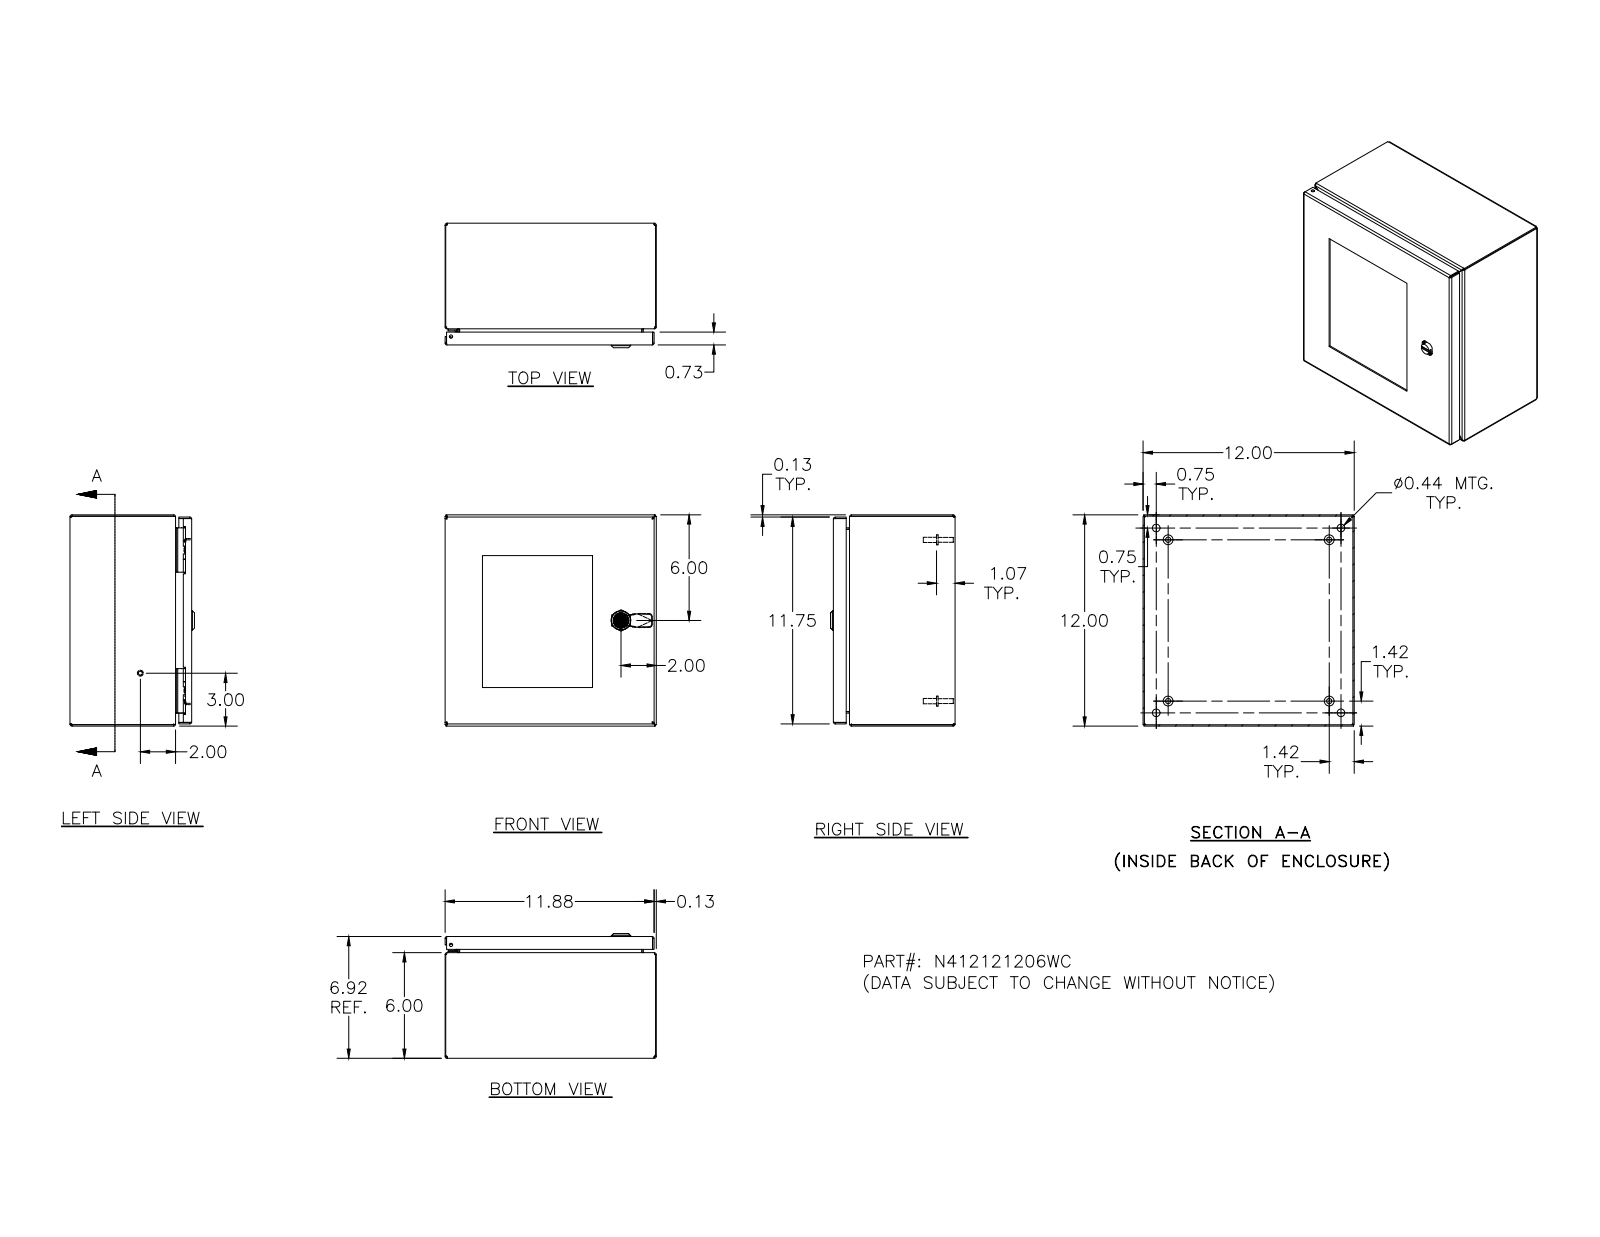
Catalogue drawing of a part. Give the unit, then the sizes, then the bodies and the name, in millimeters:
Units: millimetres
Overall size (bounding box): 304.8 × 304.8 × 179.7
Round holes (diameter × count): ⌀4 ×10, ⌀7.1 ×8, ⌀4.8 ×5, ⌀2.4 ×4, ⌀3.9 ×4, ⌀4.2 ×4, ⌀4.4 ×4, ⌀11.1 ×4, ⌀4.7 ×1, ⌀5 ×1, ⌀8 ×1, ⌀10 ×1
Round bosses / shafts (diameter × count): ⌀6.4 ×10, ⌀8.6 ×8, ⌀4.8 ×8, ⌀14.3 ×4, ⌀9.1 ×4, ⌀8.1 ×4, ⌀7.6 ×4, ⌀7 ×4
Partial cylindrical surfaces — rounded edges, fillets, slot ends (radius × count): R0.8 ×34, R0.3 ×30, R1.3 ×26, R2.7 ×24, R0.4 ×18, R3.2 ×16, R0.5 ×13, R0.8 ×8
Main face-to-face distances: 1.9, 302.9, 173.8, 171.9, 301, 304.8, 175.7, 6.4, 167.5, 165.6
Hole centre spacings: 203.2, 101.6, 158, 218.1, 266.7, 226.7, 12.7, 16.7
Volume: 1 068 000 mm³ · Surface area: 966 400 mm²
Bodies: 53 solids, 1763 faces (665 planar, 585 cylindrical, 513 other)
Part name (STEP PRODUCT): N412121206WC
STEP written by: SolidWorks 2018 (AUTOMOTIVE_DESIGN)
